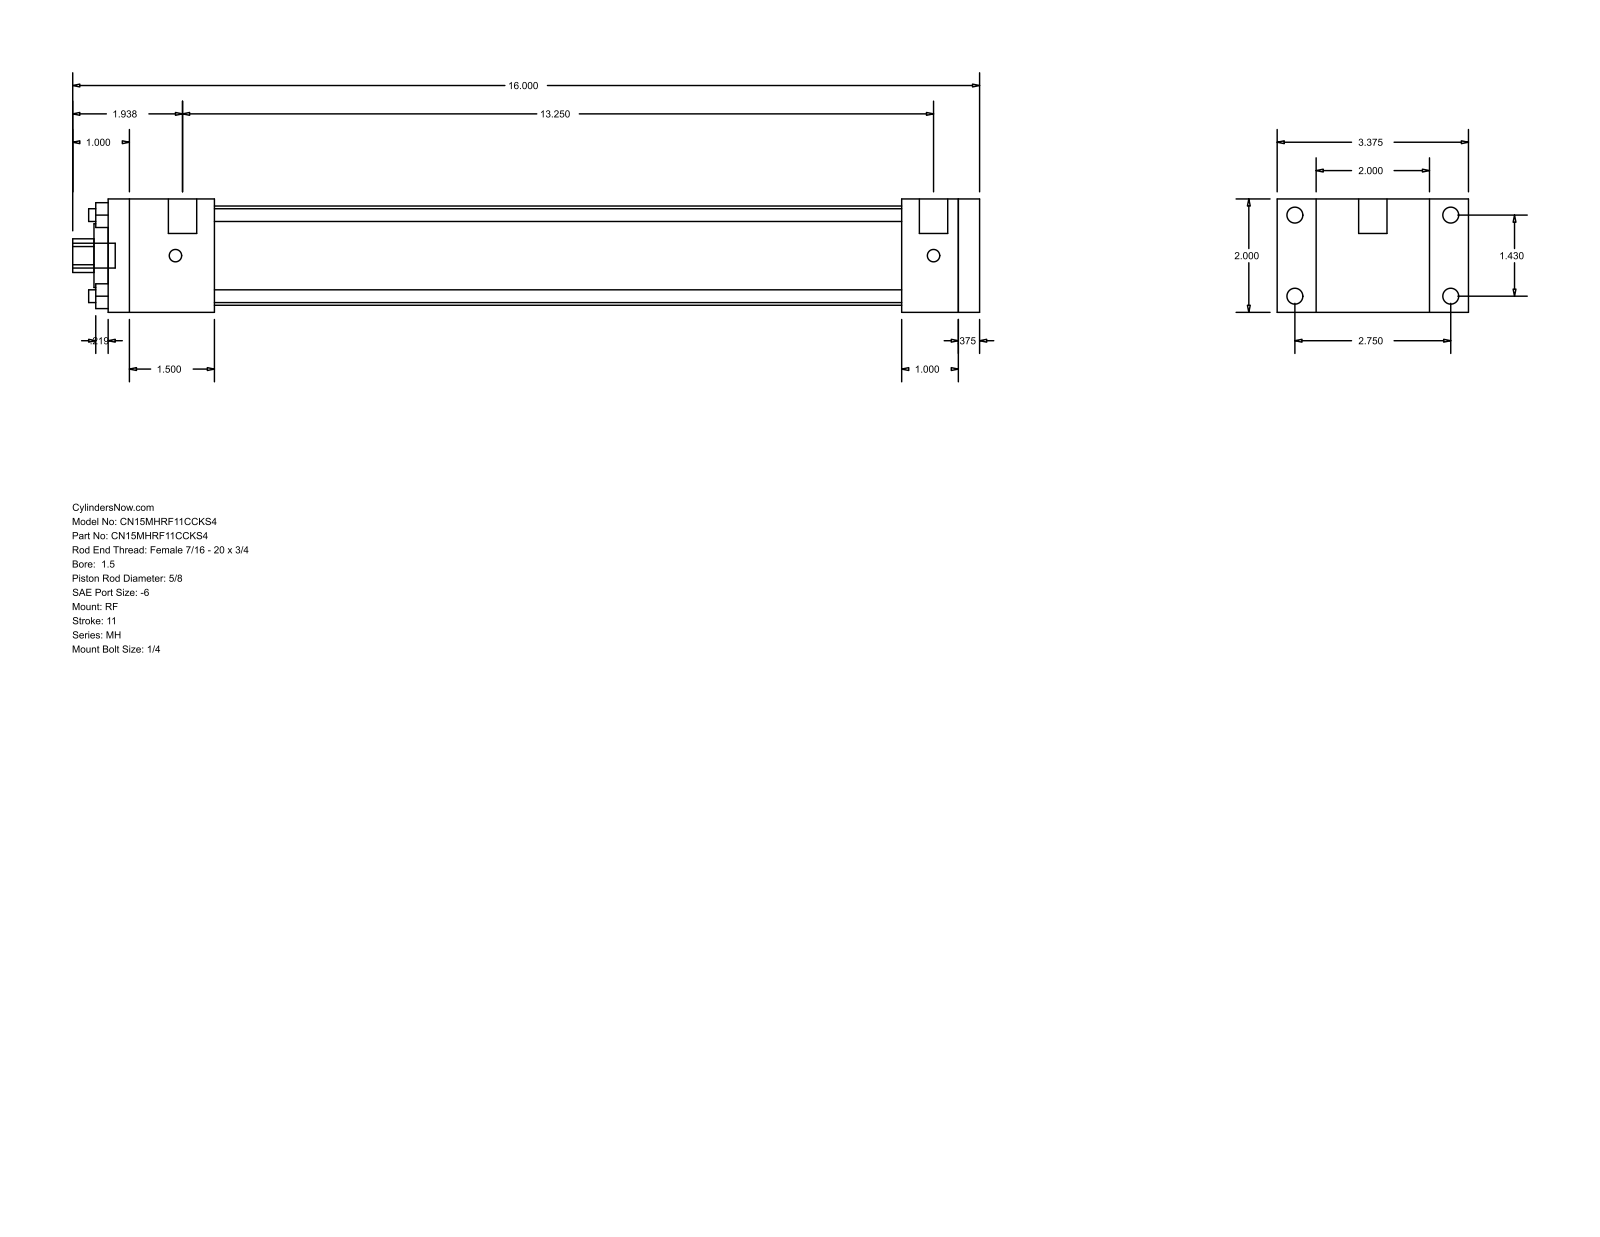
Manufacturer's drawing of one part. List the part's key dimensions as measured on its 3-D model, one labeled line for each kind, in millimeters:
Part name (STEP PRODUCT): MH_RF__0150_0.625
STEP written by: GSSL Pune (CONFIG_CONTROL_DESIGN)
Units: millimetres
Bodies: 0 solids, 92 faces (64 planar, 28 cylindrical, 0 other)
Overall size (bounding box): 406.4 × 85.72 × 50.8
Round holes (diameter × count): ⌀5.71 ×4, ⌀15.88 ×1, ⌀28.57 ×1, ⌀44.45 ×1
Round bosses / shafts (diameter × count): ⌀7.14 ×4, ⌀5.56 ×4, ⌀12.7 ×2, ⌀11.11 ×1
Partial cylindrical surfaces — rounded edges, fillets, slot ends (radius × count): R7.54 ×1
Main face-to-face distances: 50.8, 9.52, 381, 390.52, 17.46, 68.26, 355.6, 25.4, 34.92, 47.62
Hole centre spacings: 25.68, 36.32, 51.36
